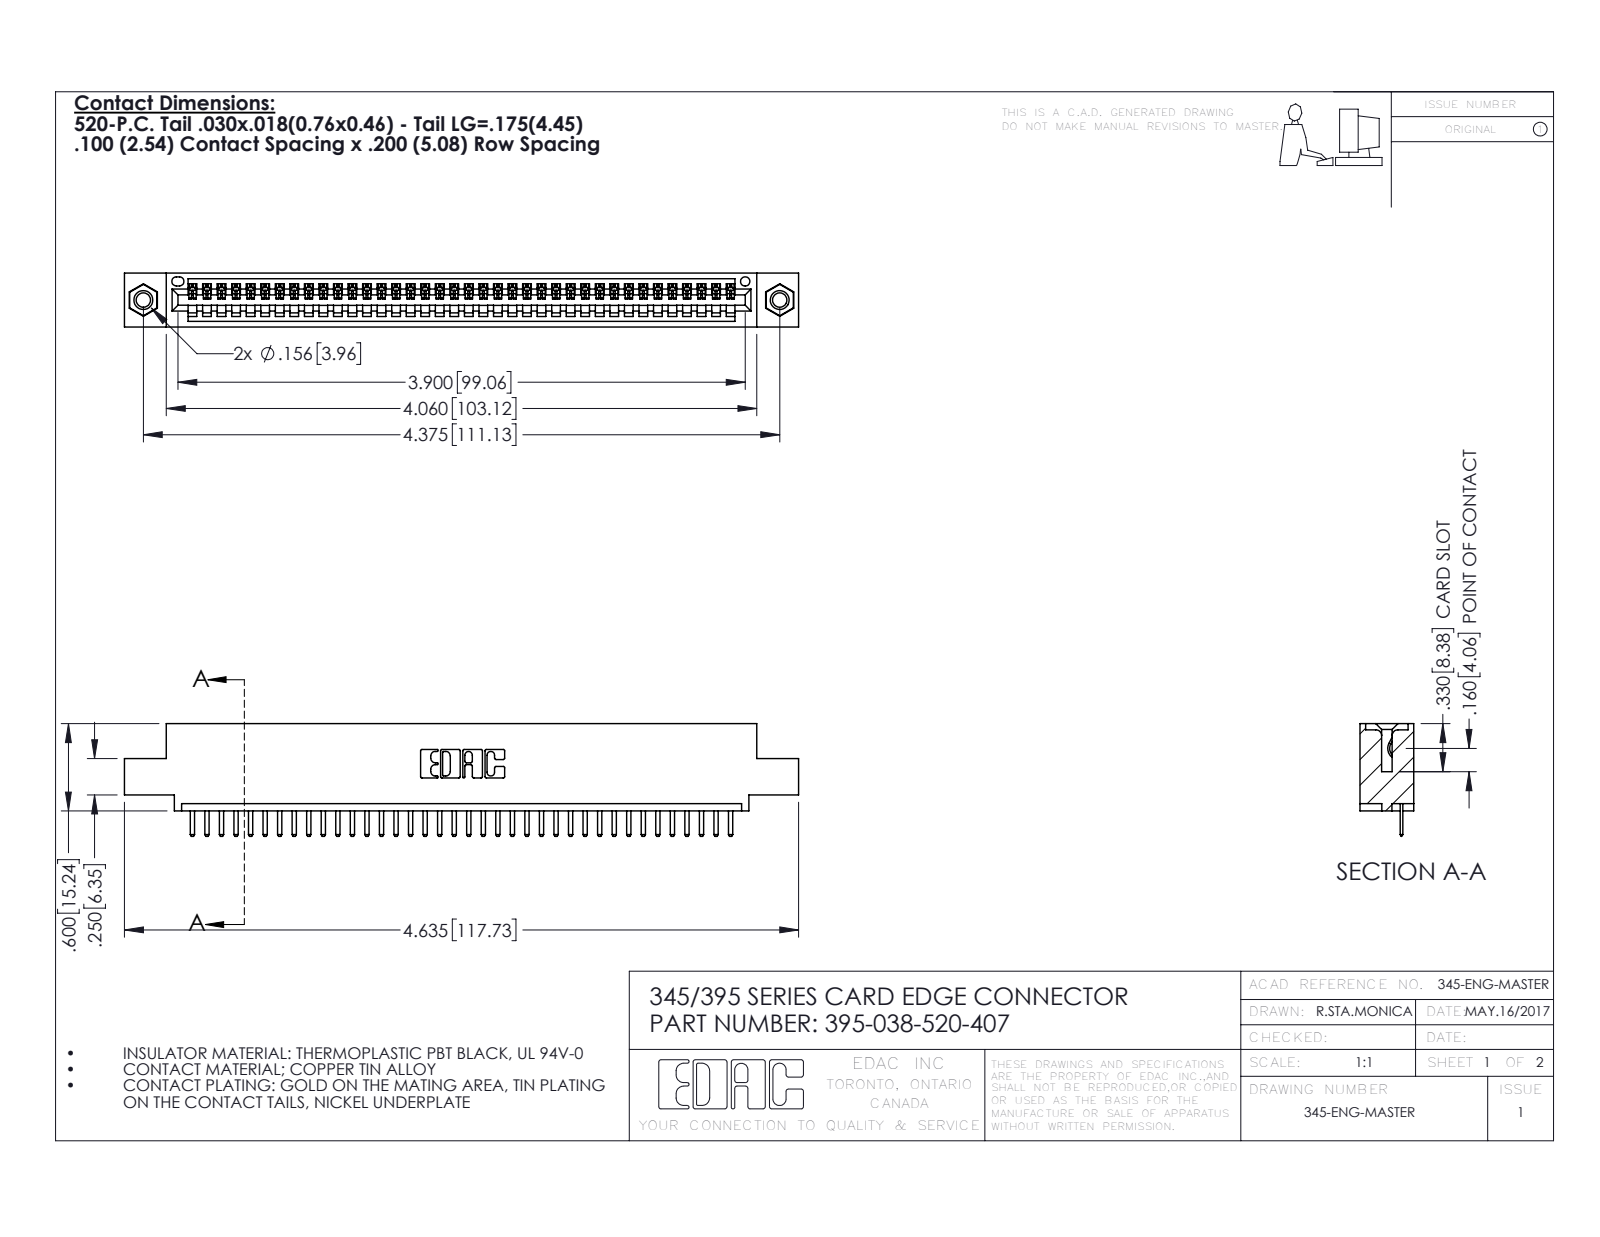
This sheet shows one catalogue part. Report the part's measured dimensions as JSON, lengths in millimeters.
{"part_name": "345 Part_0.110 Offset - 0.156 Dia-TI; 345-250-001_345-250-005-103; 345-292-001_345-293-120; 395-038-520-407", "step_written_by": "SolidWorks 2016 (CONFIG_CONTROL_DESIGN)", "units": "millimeters", "bodies": {"solids": 41, "faces": 2546, "planar": 1712, "cylindrical": 818, "other": 16}, "overall_size": [117.7, 19.7, 9.4], "volume_mm3": 10900, "surface_area_mm2": 14260, "round_holes": [[2.5, 2], [3.2, 2], [4, 2], [1.6, 1]], "round_bosses_or_shafts": [[3.9, 2]], "partial_cylinders_radius": [[0.3, 78], [0.2, 76], [0.3, 22], [0.2, 6], [0.8, 6], [0.7, 3], [0.8, 2], [1, 2]], "face_to_face_distances": [1.8, 7.6, 9.4, 5.1, 2.5, 6.9, 0.6, 5.7, 1.8, 3.8], "hole_center_spacings": [6.9, 105.1, 111.1]}
